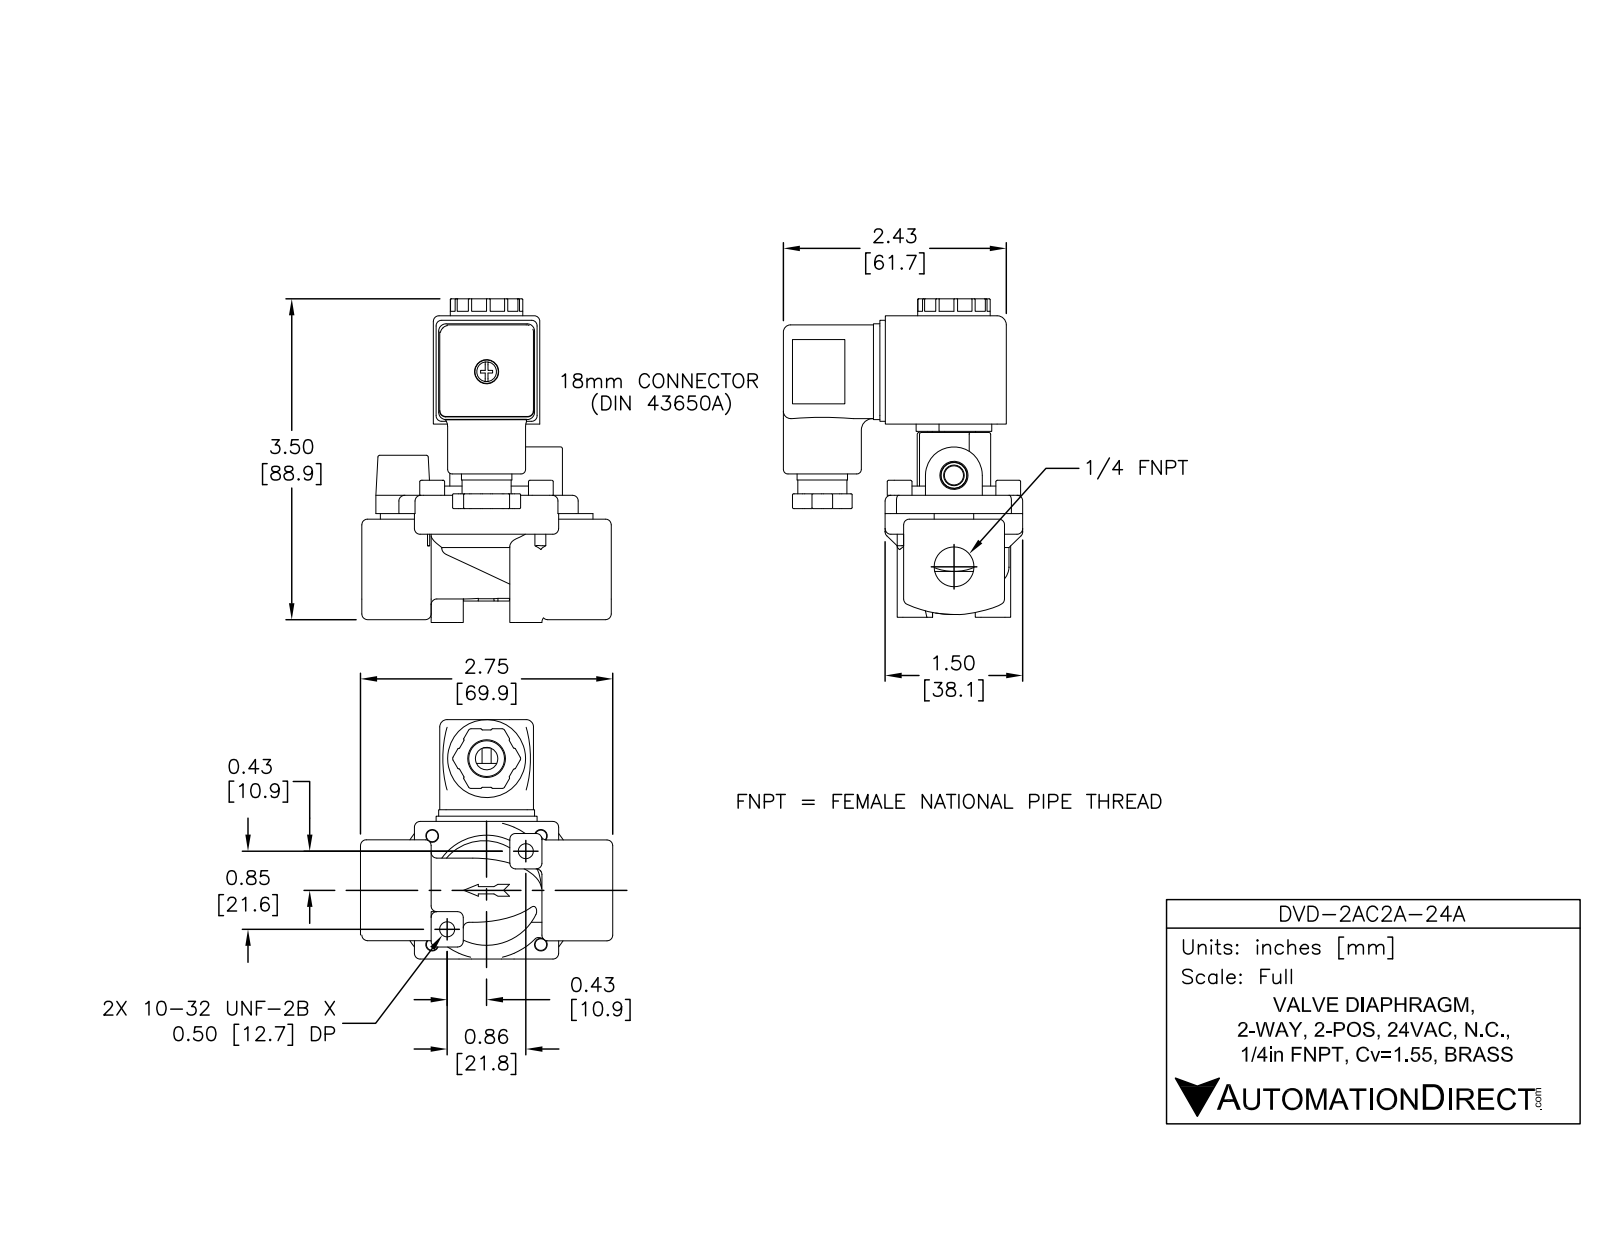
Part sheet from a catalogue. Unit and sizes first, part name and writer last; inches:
Units: inches
Overall size (bounding box): 3.472 × 2.72 × 2.61
Round holes (diameter × count): ⌀0.139 ×4, ⌀0.06 ×2, ⌀0.098 ×2, ⌀0.14 ×2, ⌀0.164 ×2, ⌀0.434 ×2, ⌀0.062 ×1, ⌀0.077 ×1, ⌀0.089 ×1, ⌀0.093 ×1, ⌀0.102 ×1, ⌀0.12 ×1
Round bosses / shafts (diameter × count): ⌀0.27 ×4, ⌀0.16 ×4, ⌀1.375 ×1, ⌀0.85 ×1, ⌀0.79 ×1, ⌀0.609 ×1, ⌀0.535 ×1, ⌀0.405 ×1
Partial cylindrical surfaces — rounded edges, fillets, slot ends (radius × count): R0.01 ×52, R0.063 ×29, R0.062 ×21, R0.08 ×12, R0.156 ×12, R0.05 ×8, R0.062 ×7, R0.03 ×6
Main face-to-face distances: 0.925, 1.161, 0.2, 0.08, 1.036, 1.1, 1.181, 0.956, 1.3, 0.06
Hole centre spacings: 0.924, 0.838, 1.185, 0.233, 0.389, 0.449, 0.605, 0.672
Volume: 5.884 in³ · Surface area: 63.91 in²
Bodies: 1 solid, 1779 faces (848 planar, 363 cylindrical, 568 other)
Part name (STEP PRODUCT): DVD-2AC2A-24A
STEP written by: SolidWorks 2015 (AUTOMOTIVE_DESIGN)
